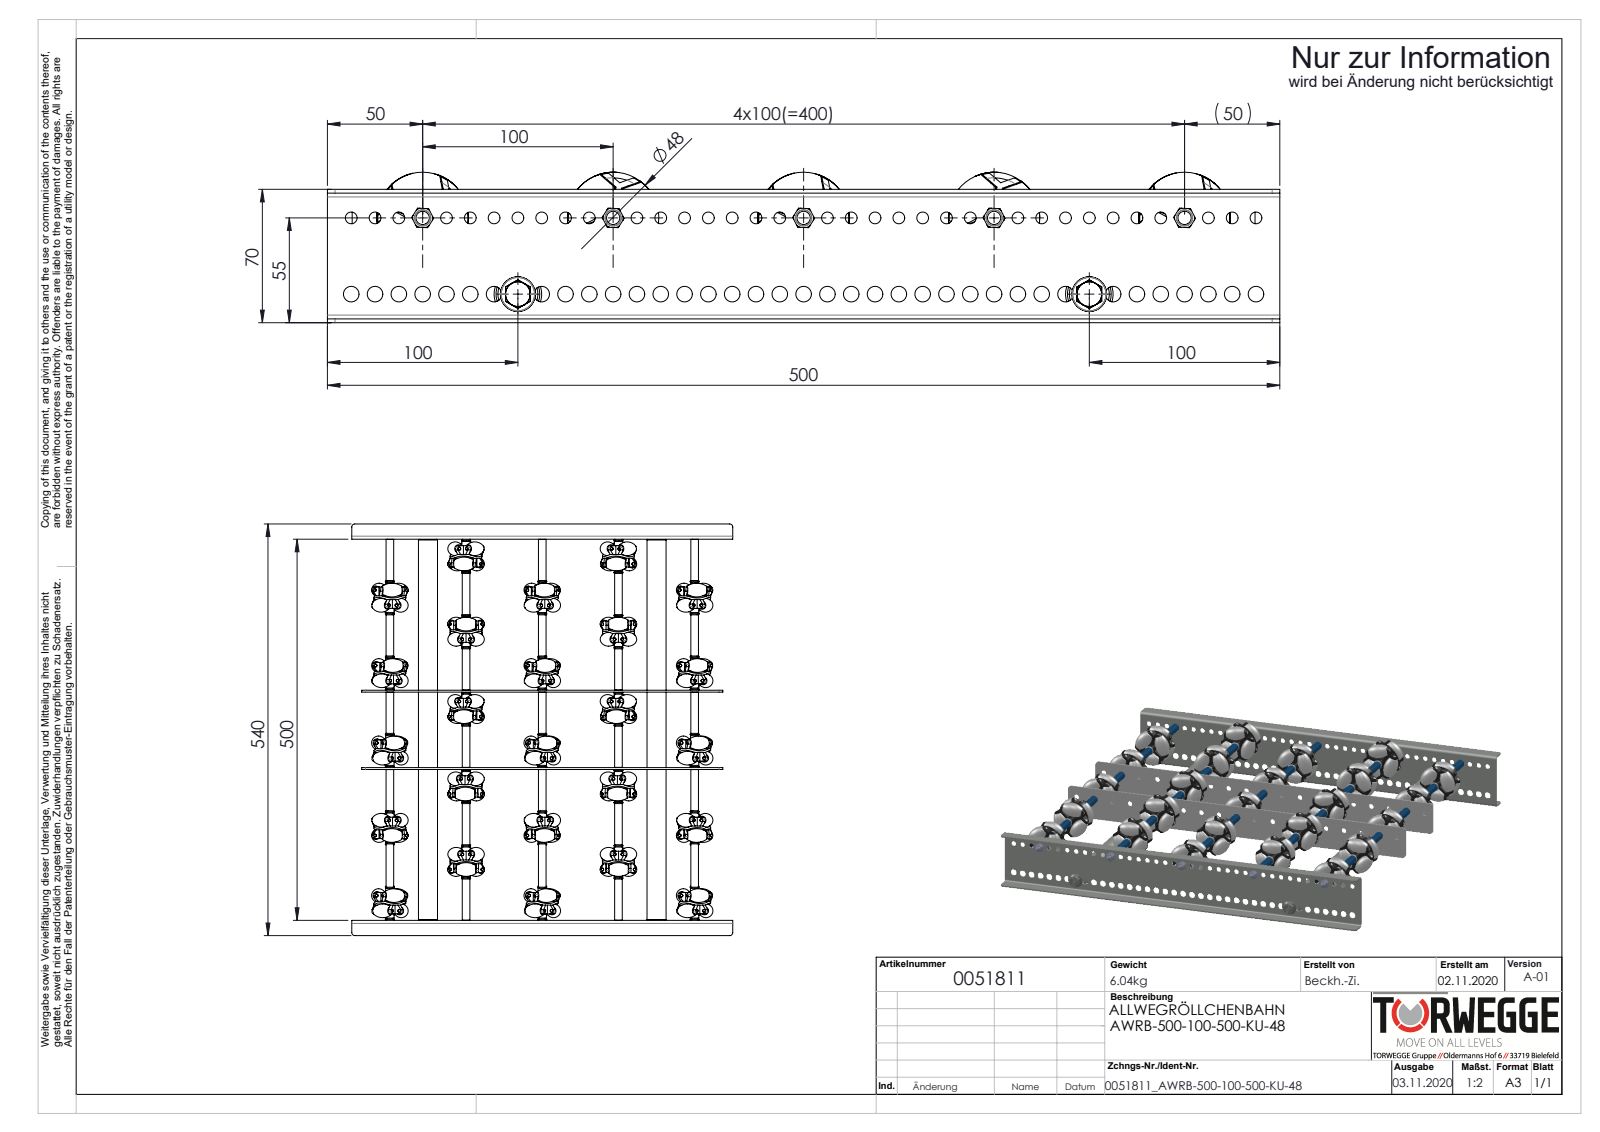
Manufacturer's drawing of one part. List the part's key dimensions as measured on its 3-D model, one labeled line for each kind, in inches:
Part name (STEP PRODUCT): Traversen_KFG_L500; 0027528_BUCHSE-HOHLNIETE ZU AWR48; AWR48_Halter; Profil-RB-20x70x20x2_S100208_U-PROFIL-20-70-20-2-RB-L=500 (+8 more)
STEP written by: SolidWorks 2020 (AUTOMOTIVE_DESIGN)
Units: inches
Bodies: 429 solids, 7818 faces (2672 planar, 3102 cylindrical, 2044 other)
Overall size (bounding box): 21.26 × 19.685 × 3.11
Volume: 101.4 in³ · Surface area: 1 862 in²
Round holes (diameter × count): ⌀0.146 ×150, ⌀0.165 ×150, ⌀0.244 ×39, ⌀0.323 ×39, ⌀0.256 ×19, ⌀0.194 ×5, ⌀0.331 ×5, ⌀0.268 ×2, ⌀0.827 ×2
Round bosses / shafts (diameter × count): ⌀0.157 ×150, ⌀0.146 ×125, ⌀0.315 ×7, ⌀1.654 ×5, ⌀0.433 ×5, ⌀0.394 ×5, ⌀0.276 ×5, ⌀0.236 ×5
Partial cylindrical surfaces — rounded edges, fillets, slot ends (radius × count): R0.157 ×8, R0.927 ×5, R0.079 ×4, R0.197 ×4
Main face-to-face distances: 0.079, 19.764, 3.996, 0.098, 2.677, 19.685, 19.843, 0.581, 0.118, 3.898
Hole centre spacings: 1.42, 1.419, 0.492, 0.984, 1.476, 1.419, 1.969, 2.461
